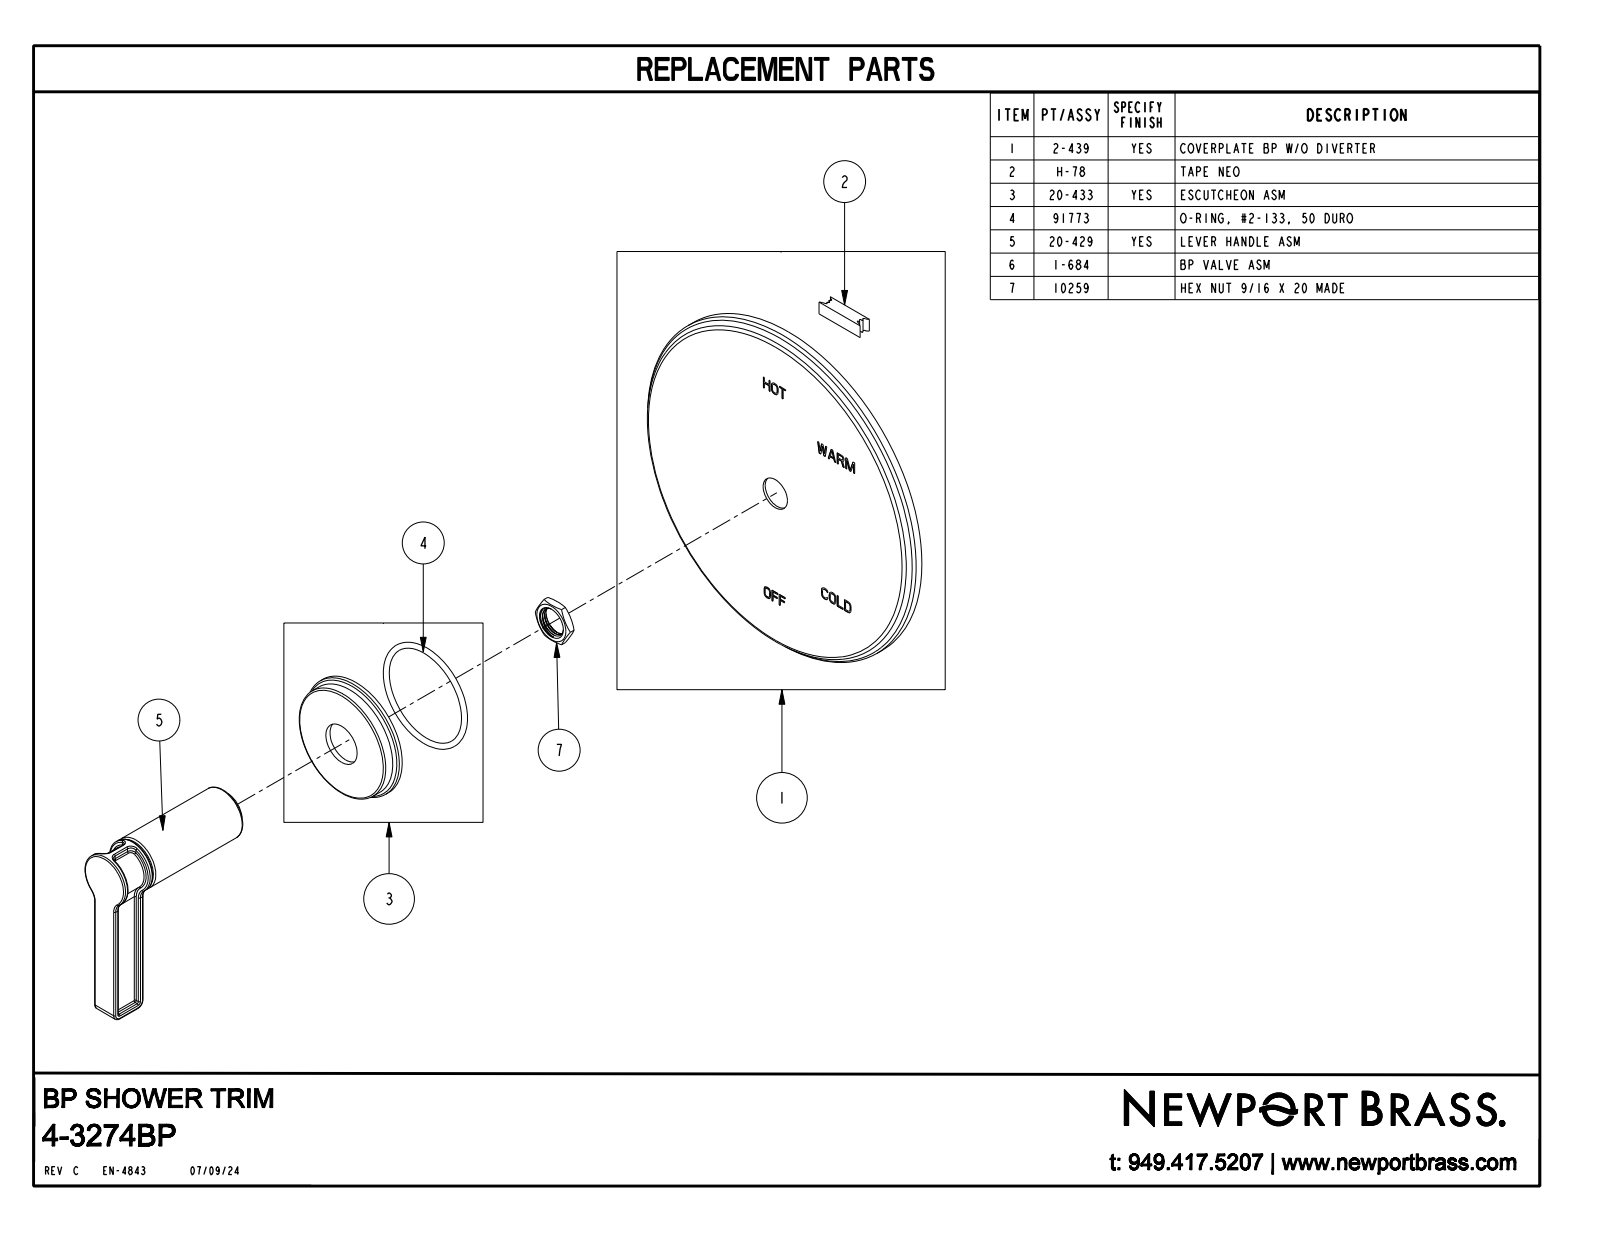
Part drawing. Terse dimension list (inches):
name: 11117; H-78; 2-439_ASM; 13130 (+8 more)
written by: CREO PARAMETRIC BY PTC INC, 2018400 (CONFIG_CONTROL_DESIGN)
unit: in
bodies: 12 solids, 1121 faces (524 planar, 357 cylindrical, 240 other)
size: 6.5 × 6.5 × 3.564
volume: 4.89 in³; area: 179.8 in²
holes: 1× ⌀0.11, 1× ⌀0.168, 1× ⌀0.275, 1× ⌀0.358, 1× ⌀0.36, 1× ⌀0.375, 1× ⌀0.383, 1× ⌀0.397, 1× ⌀0.4, 1× ⌀0.516, 1× ⌀0.59, 1× ⌀0.6
bosses: 1× ⌀6.5, 1× ⌀2.25, 1× ⌀2.09, 1× ⌀1.812, 1× ⌀0.975, 1× ⌀0.85, 1× ⌀0.73, 1× ⌀0.51
rounds: 22× R0.025, 6× R0.01, 6× R0.042, 4× R0.1, 2× R0.03, 2× R0.13, 2× R0.25, 2× R0.35
face distances: 0.05, 0.4, 0.35, 0.1, 2.901, 0.3, 3.301, 3.251, 2.551, 0.7
